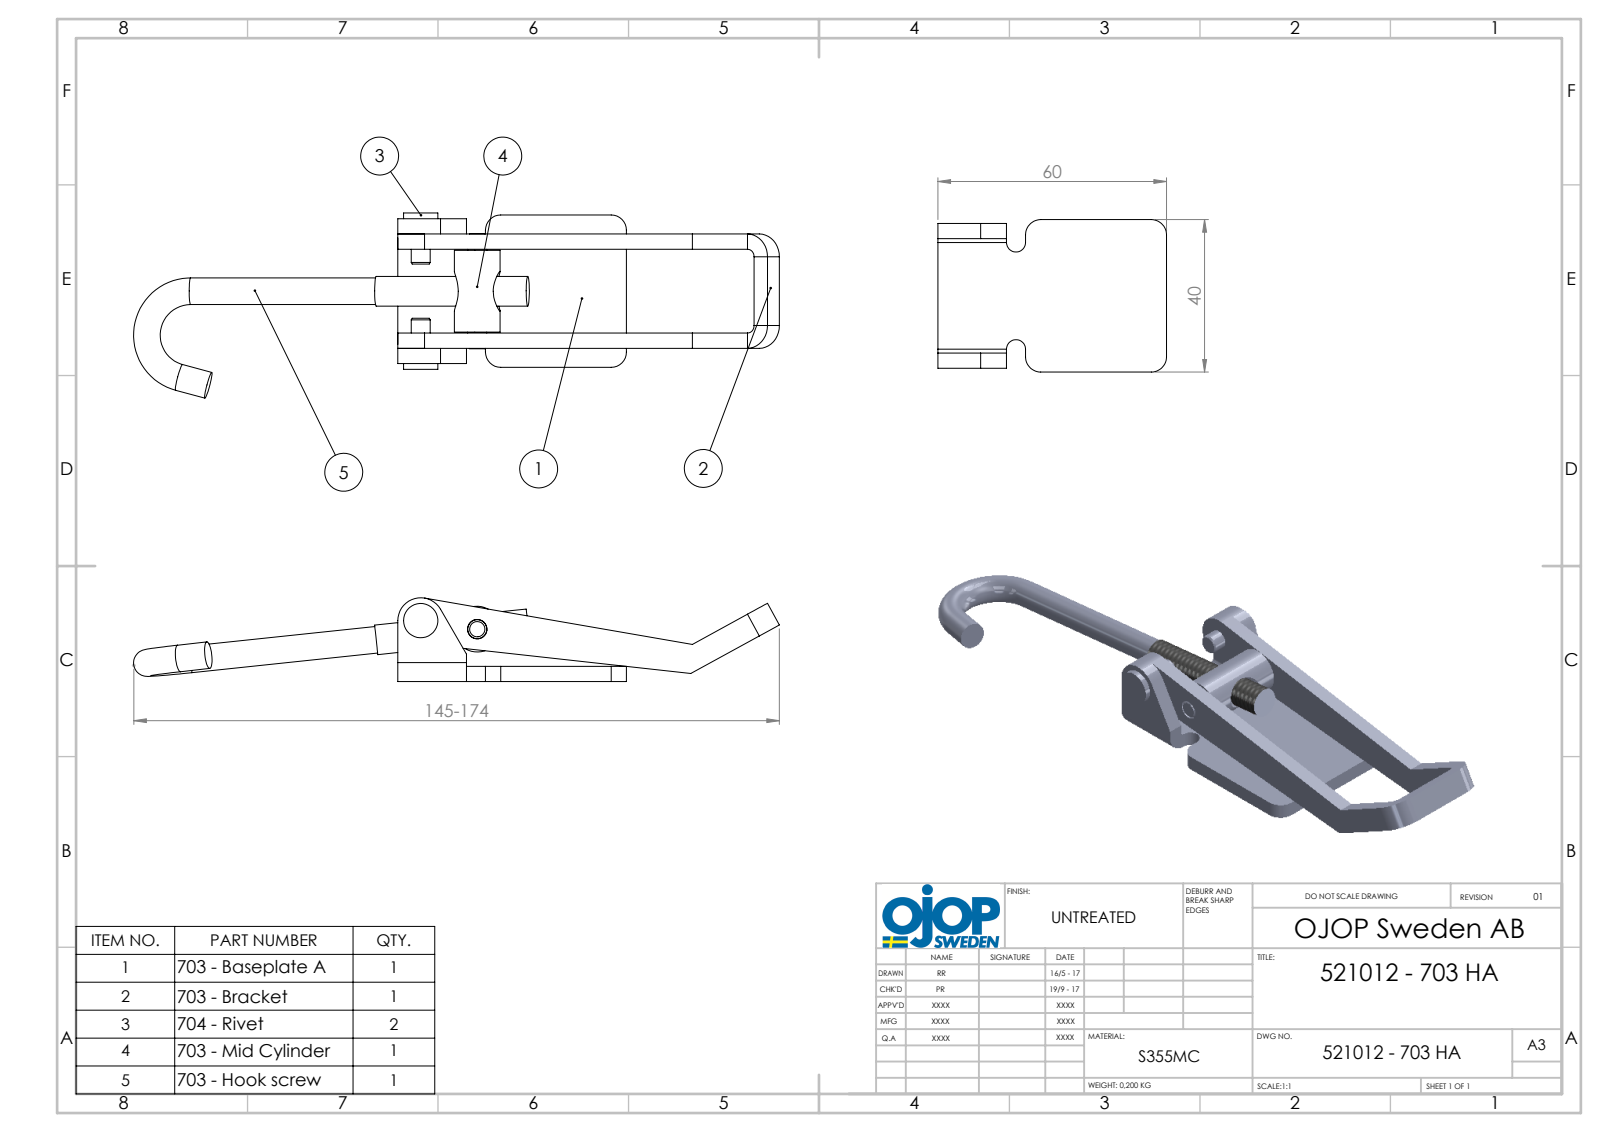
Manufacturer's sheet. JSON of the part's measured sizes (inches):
{"part_name": "703 - Platta A; 703 - Bygel; 704 - Rivet Gradin; 703 - Hake (+2 more)", "step_written_by": "SolidWorks 2015 (AUTOMOTIVE_DESIGN)", "units": "inches", "bodies": {"solids": 6, "faces": 128, "planar": 57, "cylindrical": 57, "other": 14}, "overall_size": [6.674, 1.913, 0.866], "volume_in3": 1.608, "surface_area_in2": 27.14, "round_holes": [[0.201, 2], [0.283, 1], [0.303, 1]], "round_bosses_or_shafts": [[0.276, 3], [0.197, 2], [0.472, 1], [0.354, 1], [0.307, 1]], "partial_cylinders_radius": [[0.157, 4], [0.236, 3], [0.039, 2], [0.079, 2], [0.098, 2], [0.197, 2]], "face_to_face_distances": [0.157, 1.024, 1.181, 0.866, 0.315, 1.339, 0.197, 0.039, 0.354, 1.22], "hole_center_spacings": [0.591]}
